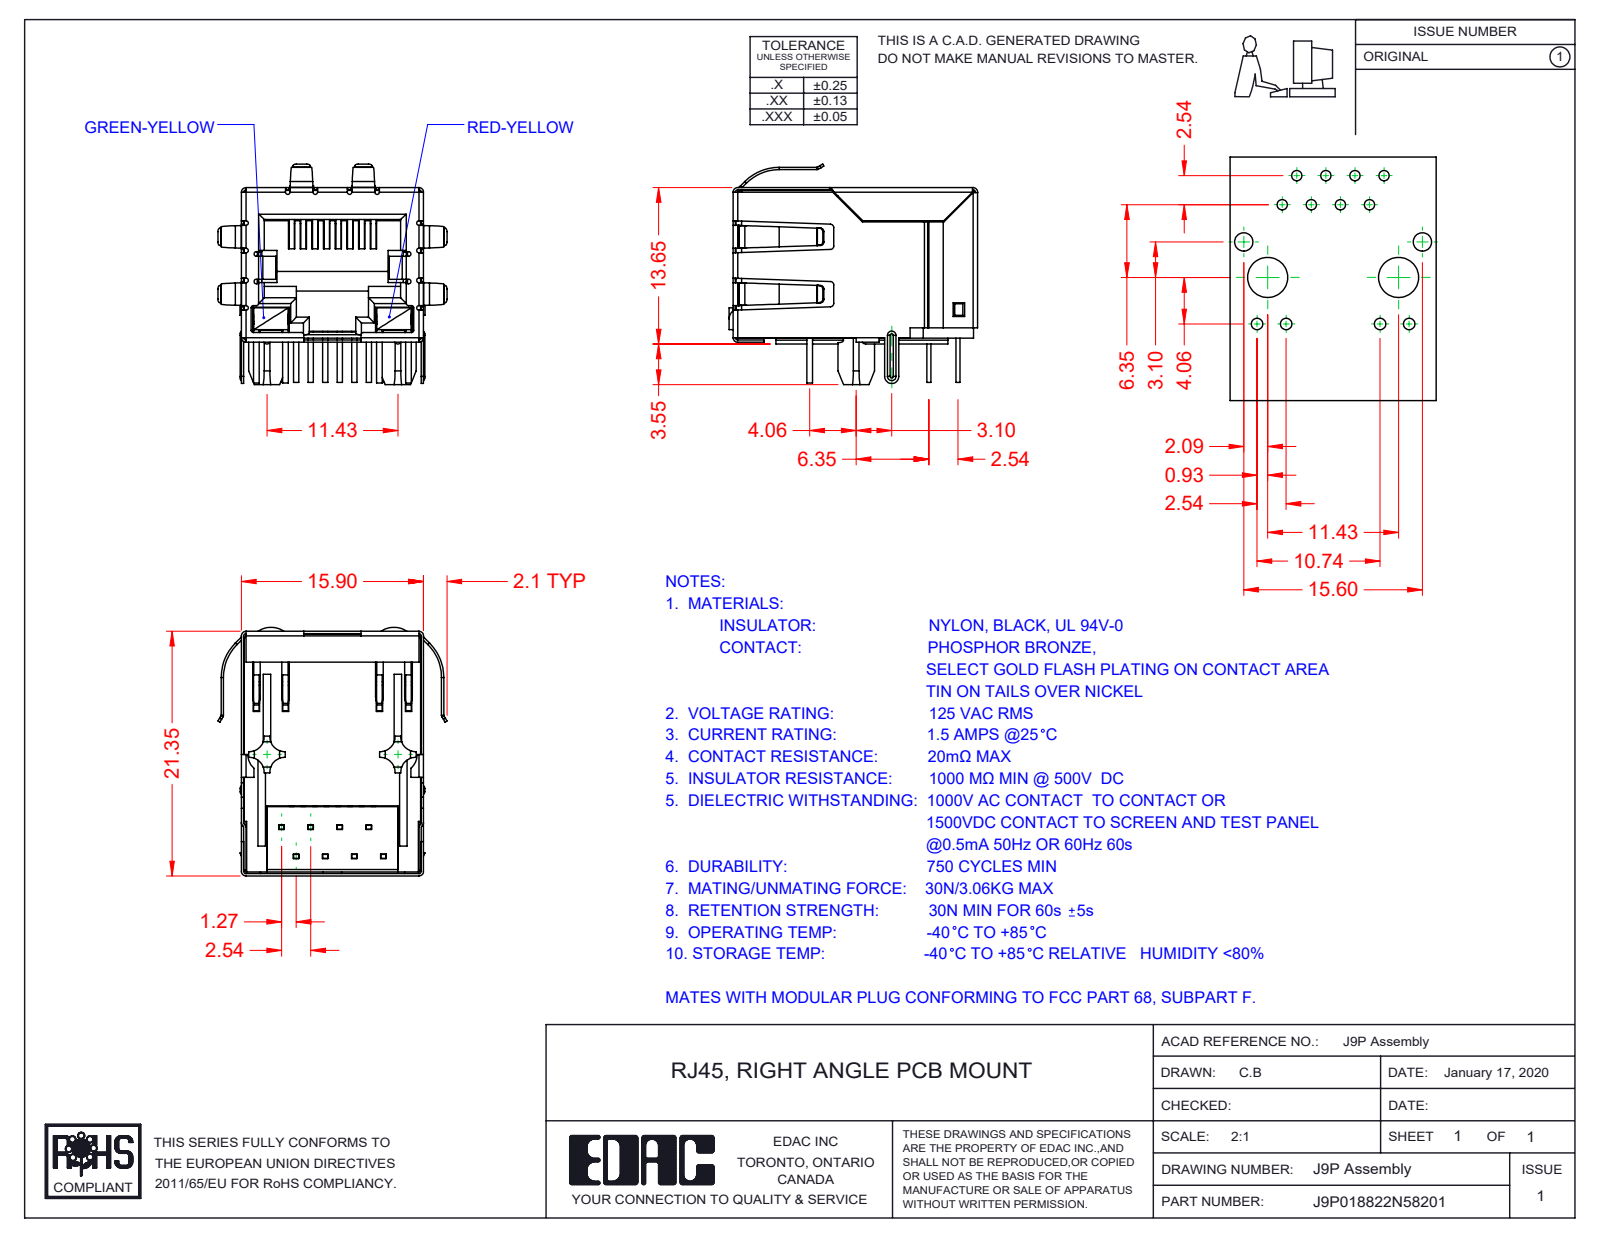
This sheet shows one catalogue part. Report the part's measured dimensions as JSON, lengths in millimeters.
{"part_name": "9P-LED Contact Lock; 9P-LED Shield; J9P018822N58202; 9P-LED LED LH_5-Green-Yellow (+4 more)", "step_written_by": "SolidWorks 2016 (CONFIG_CONTROL_DESIGN)", "units": "millimeters", "bodies": {"solids": 13, "faces": 1476, "planar": 1042, "cylindrical": 340, "other": 94}, "overall_size": [21.7, 20, 19.25], "volume_mm3": 2687, "surface_area_mm2": 7515, "partial_cylinders_radius": [[0.2, 39], [0.5, 22], [0.3, 20], [0.4, 16], [1.3, 8], [0.23, 5], [0.11, 4], [0.31, 4]], "face_to_face_distances": [15.45, 15.7, 15.65, 0.35, 0.54, 15.5, 12.36, 0.6, 1.4, 0.59]}
